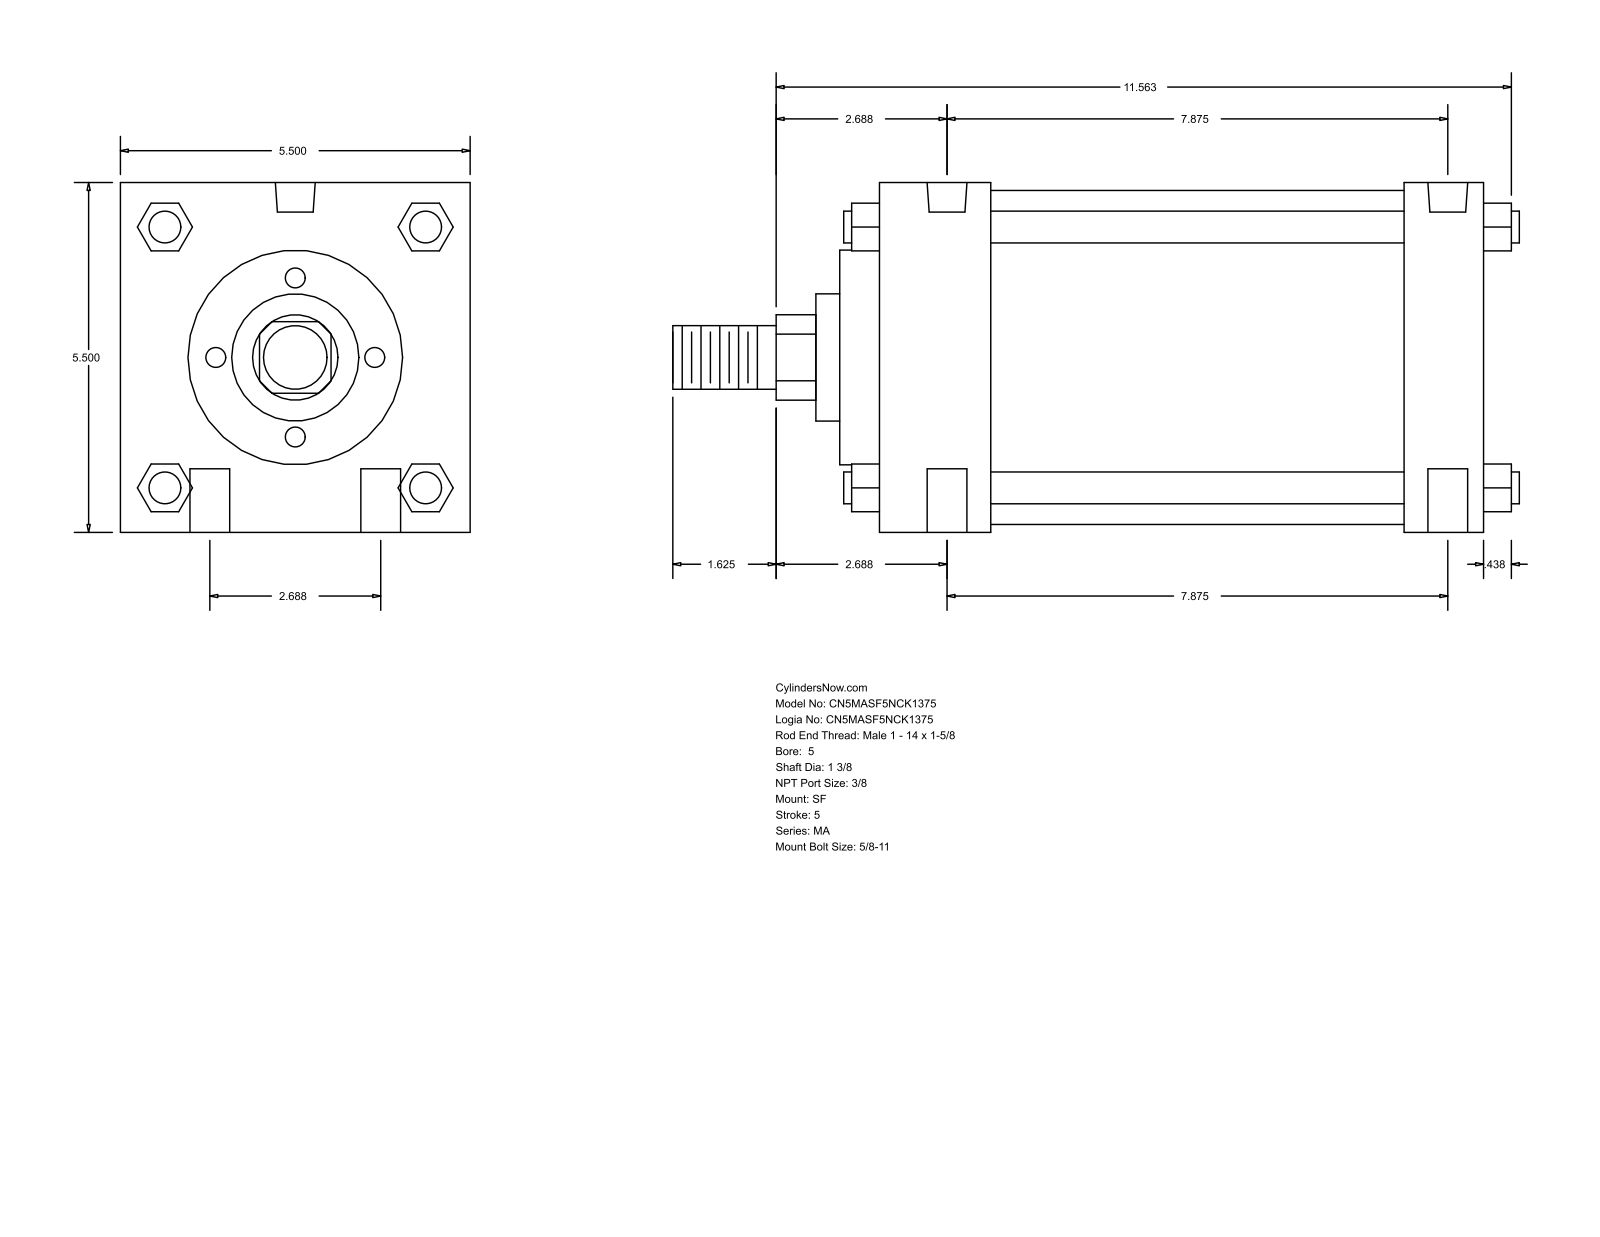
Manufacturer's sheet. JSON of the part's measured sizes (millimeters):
{"part_name": "MA_SF__0500_1.375", "step_written_by": "GSSL Pune (CONFIG_CONTROL_DESIGN)", "units": "millimeters", "bodies": {"solids": 0, "faces": 126, "planar": 95, "cylindrical": 31, "other": 0}, "overall_size": [338.14, 139.7, 139.7], "round_holes": [[15.88, 4], [11.11, 2], [15.93, 2]], "round_bosses_or_shafts": [[12.7, 4], [133.35, 1], [85.72, 1], [50.8, 1], [34.92, 1], [25.4, 1]], "partial_cylinders_radius": [[17.06, 1]], "face_to_face_distances": [139.7, 241.3, 44.45, 209.55, 165.1, 196.85, 31.75, 15.87, 60.32, 225.42], "hole_center_spacings": [34.13, 202.92, 200.03, 68.26, 211.36, 190.49]}
